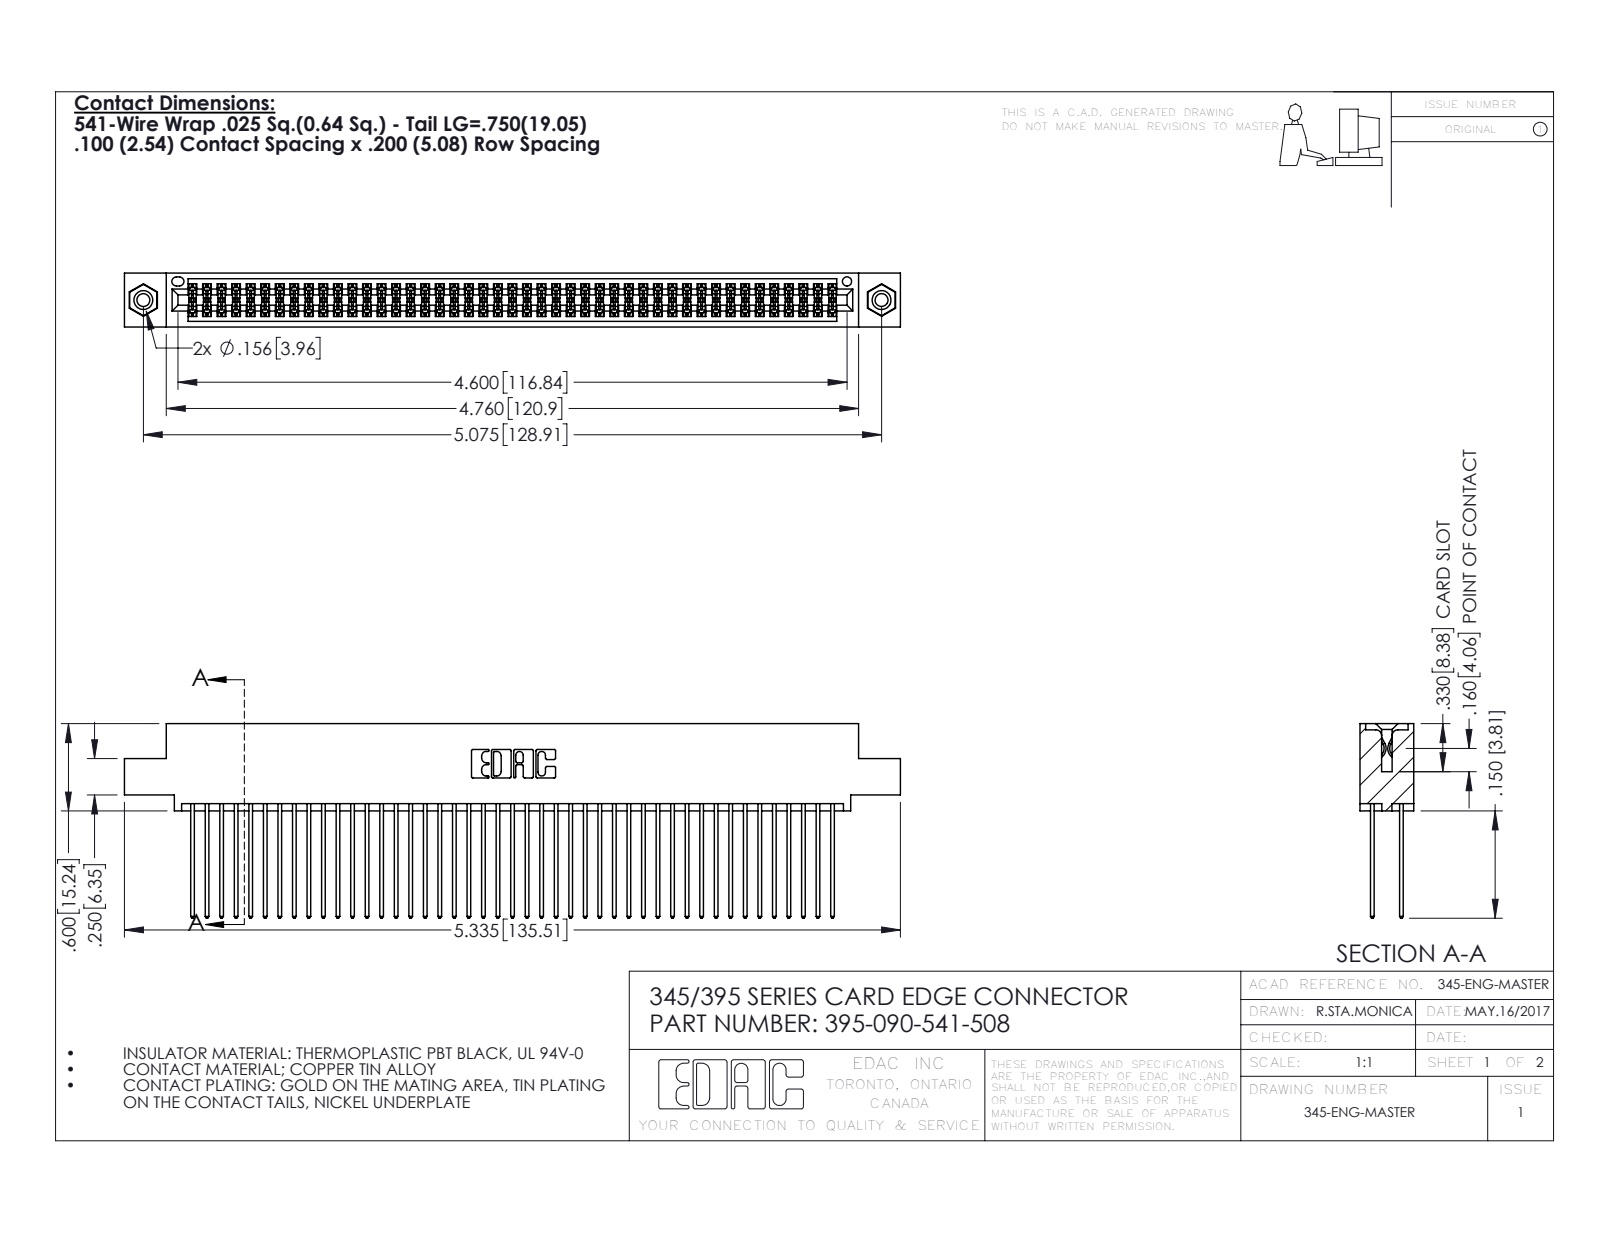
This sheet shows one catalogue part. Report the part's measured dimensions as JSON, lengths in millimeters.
{"part_name": "345-292-001_345-293-141; 345-250-001_345-250-003-102; 345 Part_0.110 Offset - 0.156 Dia-TI; 395-090-541-508", "step_written_by": "SolidWorks 2016 (CONFIG_CONTROL_DESIGN)", "units": "millimeters", "bodies": {"solids": 93, "faces": 4690, "planar": 3086, "cylindrical": 1588, "other": 16}, "overall_size": [135.5, 34, 9.4], "volume_mm3": 13600, "surface_area_mm2": 22740, "round_holes": [[2.3, 2], [3.2, 2], [4, 2], [1.6, 1]], "round_bosses_or_shafts": [[3.9, 2]], "partial_cylinders_radius": [[0.2, 135], [0.3, 90], [0.3, 22], [0.2, 6], [0.8, 6], [0.7, 3], [0.4, 2], [0.5, 2]], "face_to_face_distances": [1.8, 7.6, 5.1, 2.5, 6.9, 0.6, 5.7, 9.4, 4.4, 3.8], "hole_center_spacings": [6.9, 122.9, 128.9]}
